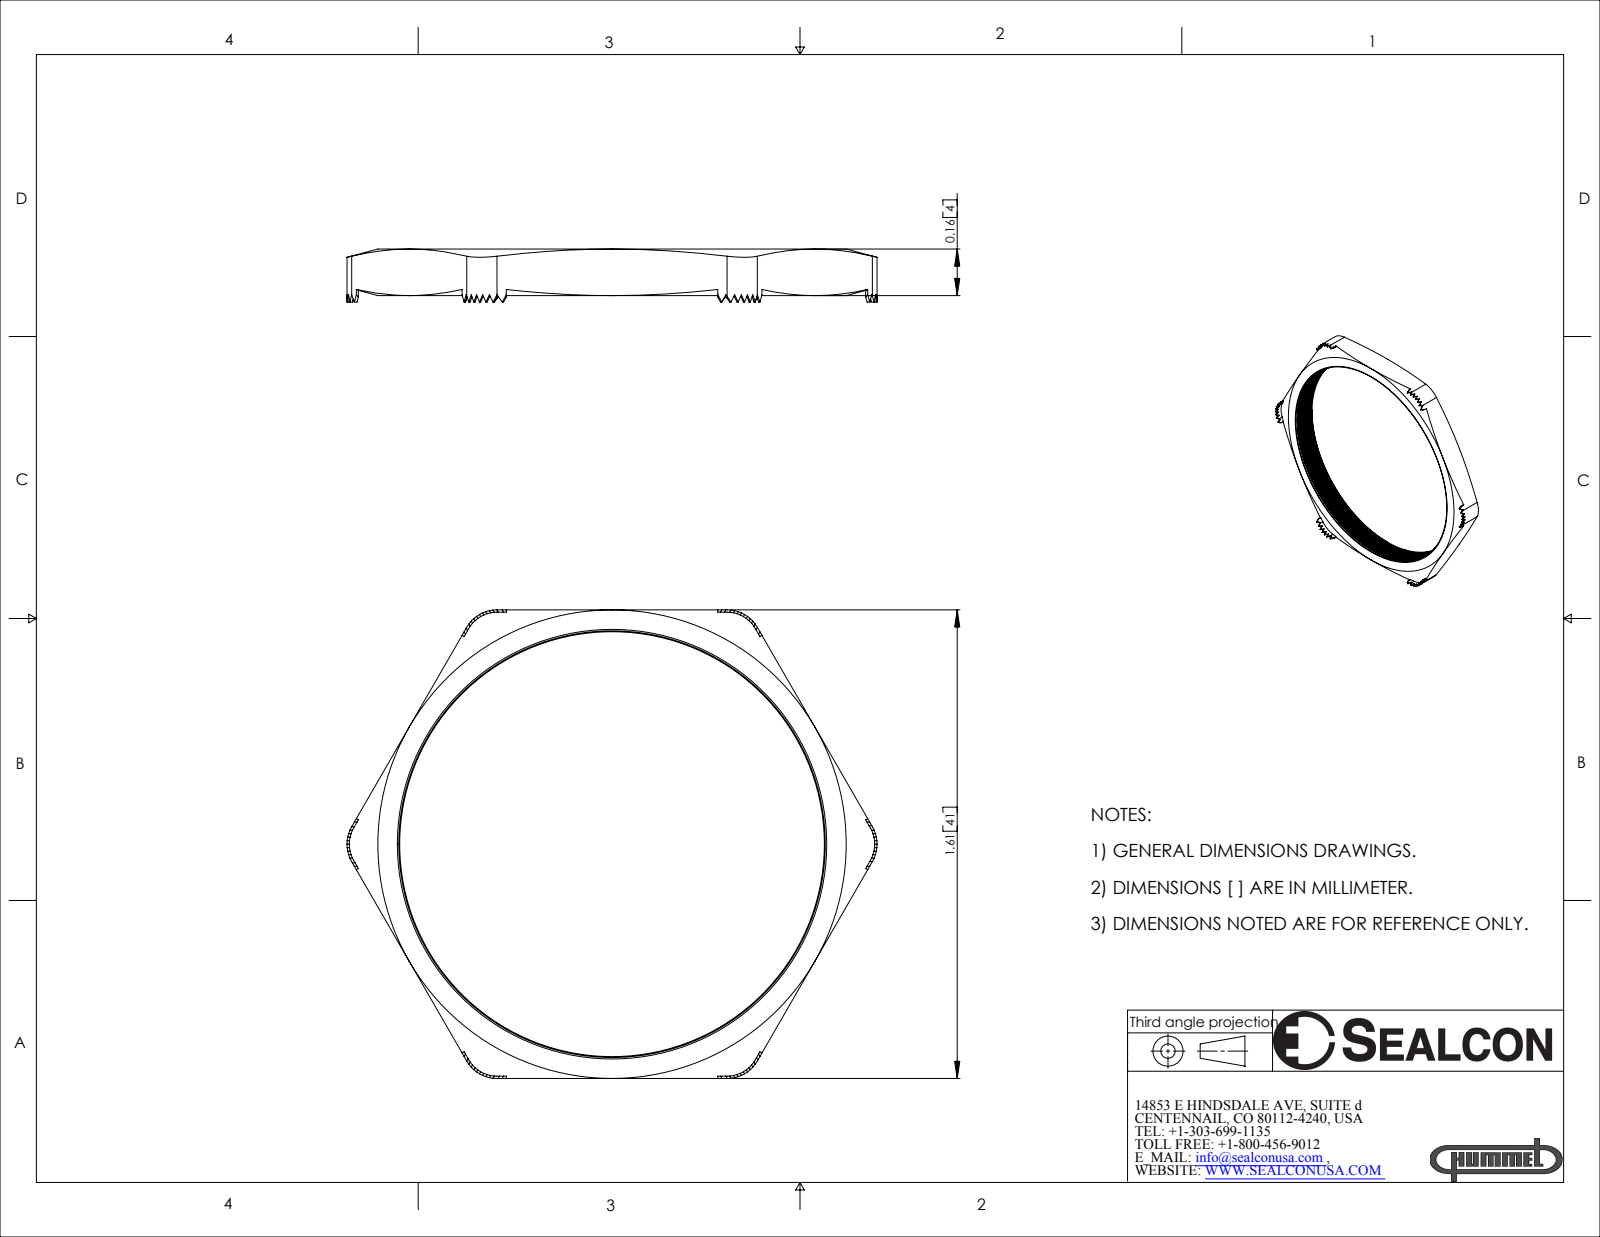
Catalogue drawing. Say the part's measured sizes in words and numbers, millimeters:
The part is named "NP-29-BE". Its 3-D file was written by "SolidWorks 2007 (CONFIG_CONTROL_DESIGN)". It is 1 solid with 224 faces: 116 planar, 38 cylindrical and 70 other. Overall it measures 46.3 by 40.9 by 4.6 millimeters. Its volume is 1 400 cubic millimeters and its surface area 2 181 square millimeters. Round holes: 1 of diameter 37.1. Partial cylindrical surfaces (rounded edges, fillets, slot ends): 6 of radius 2.8, 6 of radius 3. The main face-to-face distances are 40.9, 4.1, 40.7, 0.6, 1.1, 40.5, 1.7, 0.6, 0.5, 2.8.
